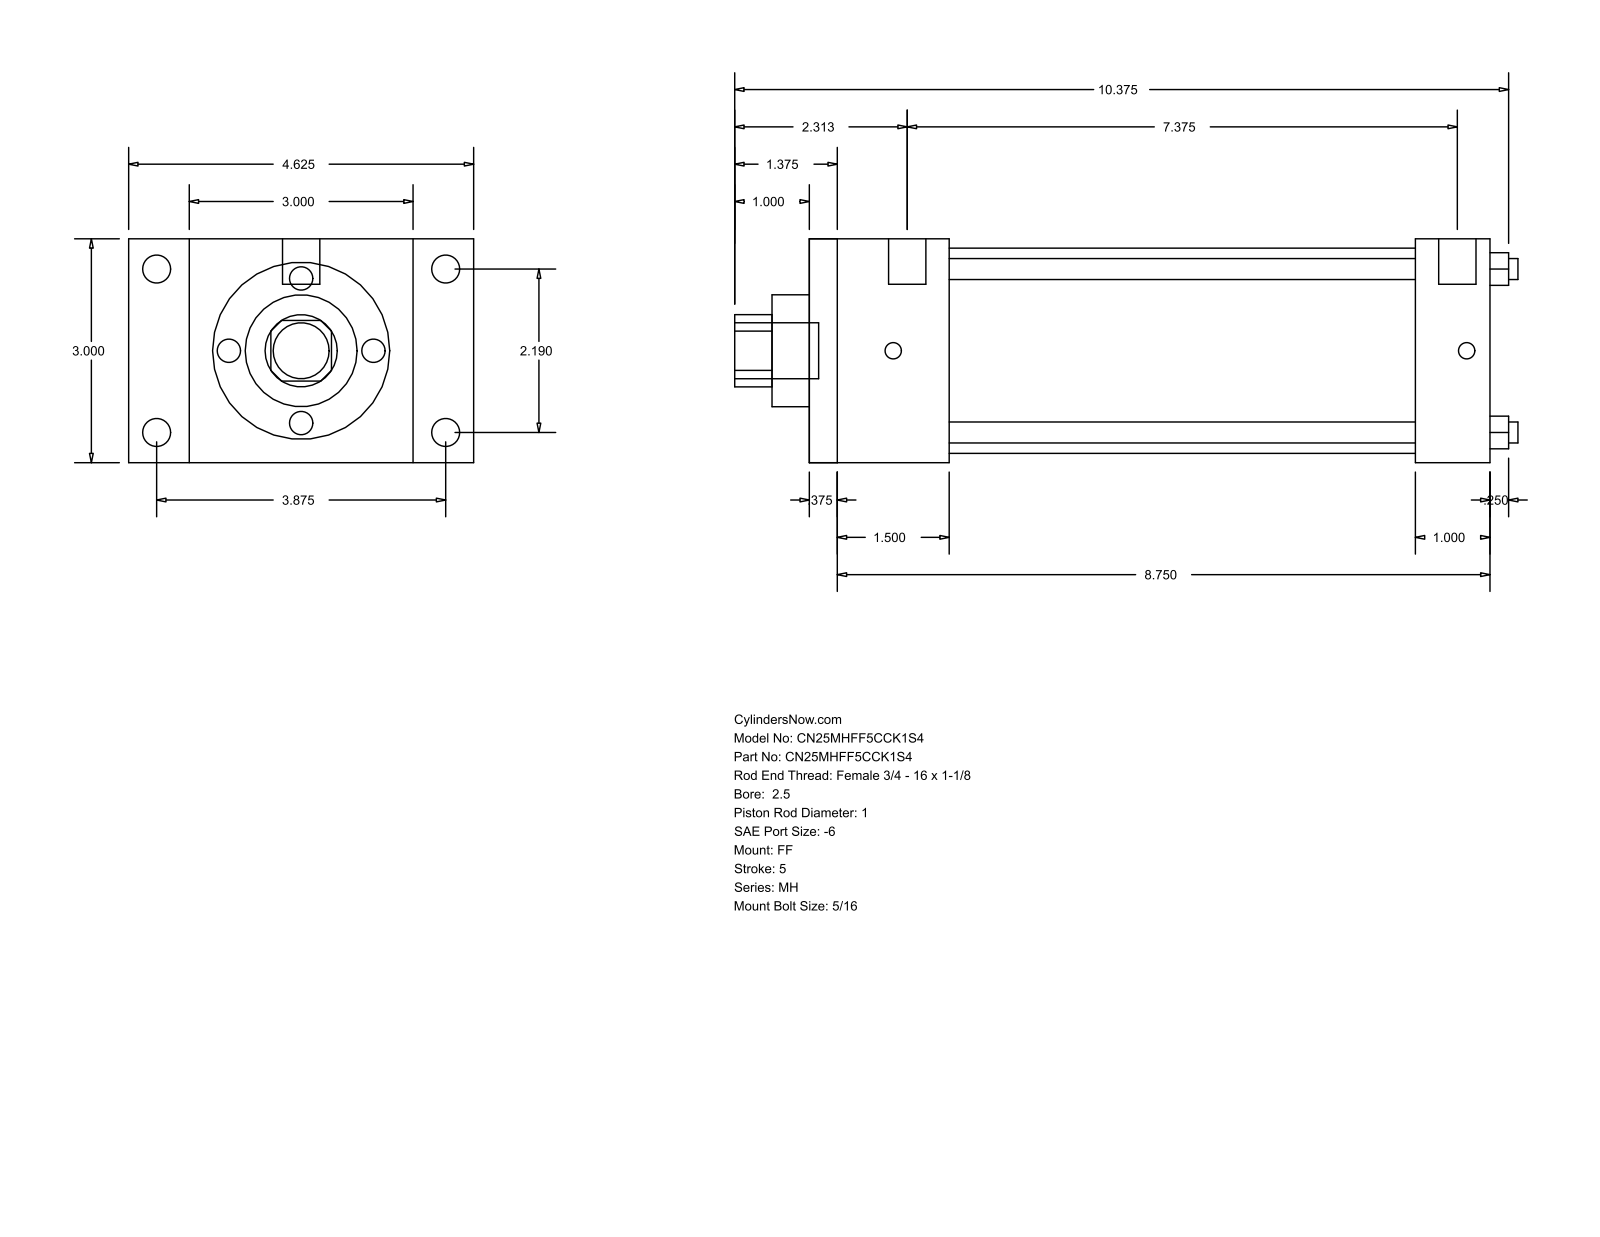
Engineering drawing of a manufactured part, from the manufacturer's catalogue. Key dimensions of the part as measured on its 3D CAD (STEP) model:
Part name (STEP PRODUCT): MH_FF__0250_1
STEP written by: GSSL Pune (CONFIG_CONTROL_DESIGN)
Units: millimetres
Bodies: 0 solids, 92 faces (64 planar, 28 cylindrical, 0 other)
Overall size (bounding box): 266.7 × 117.47 × 76.2
Round holes (diameter × count): ⌀7.14 ×4, ⌀25.4 ×1, ⌀38.1 ×1, ⌀69.85 ×1
Round bosses / shafts (diameter × count): ⌀9.53 ×4, ⌀5.56 ×4, ⌀12.7 ×2, ⌀19.05 ×1
Partial cylindrical surfaces — rounded edges, fillets, slot ends (radius × count): R12.29 ×1
Main face-to-face distances: 76.2, 231.78, 9.52, 222.26, 25.4, 47.63, 206.38, 38.11, 196.86, 158.75
Hole centre spacings: 39.33, 55.62, 78.66
